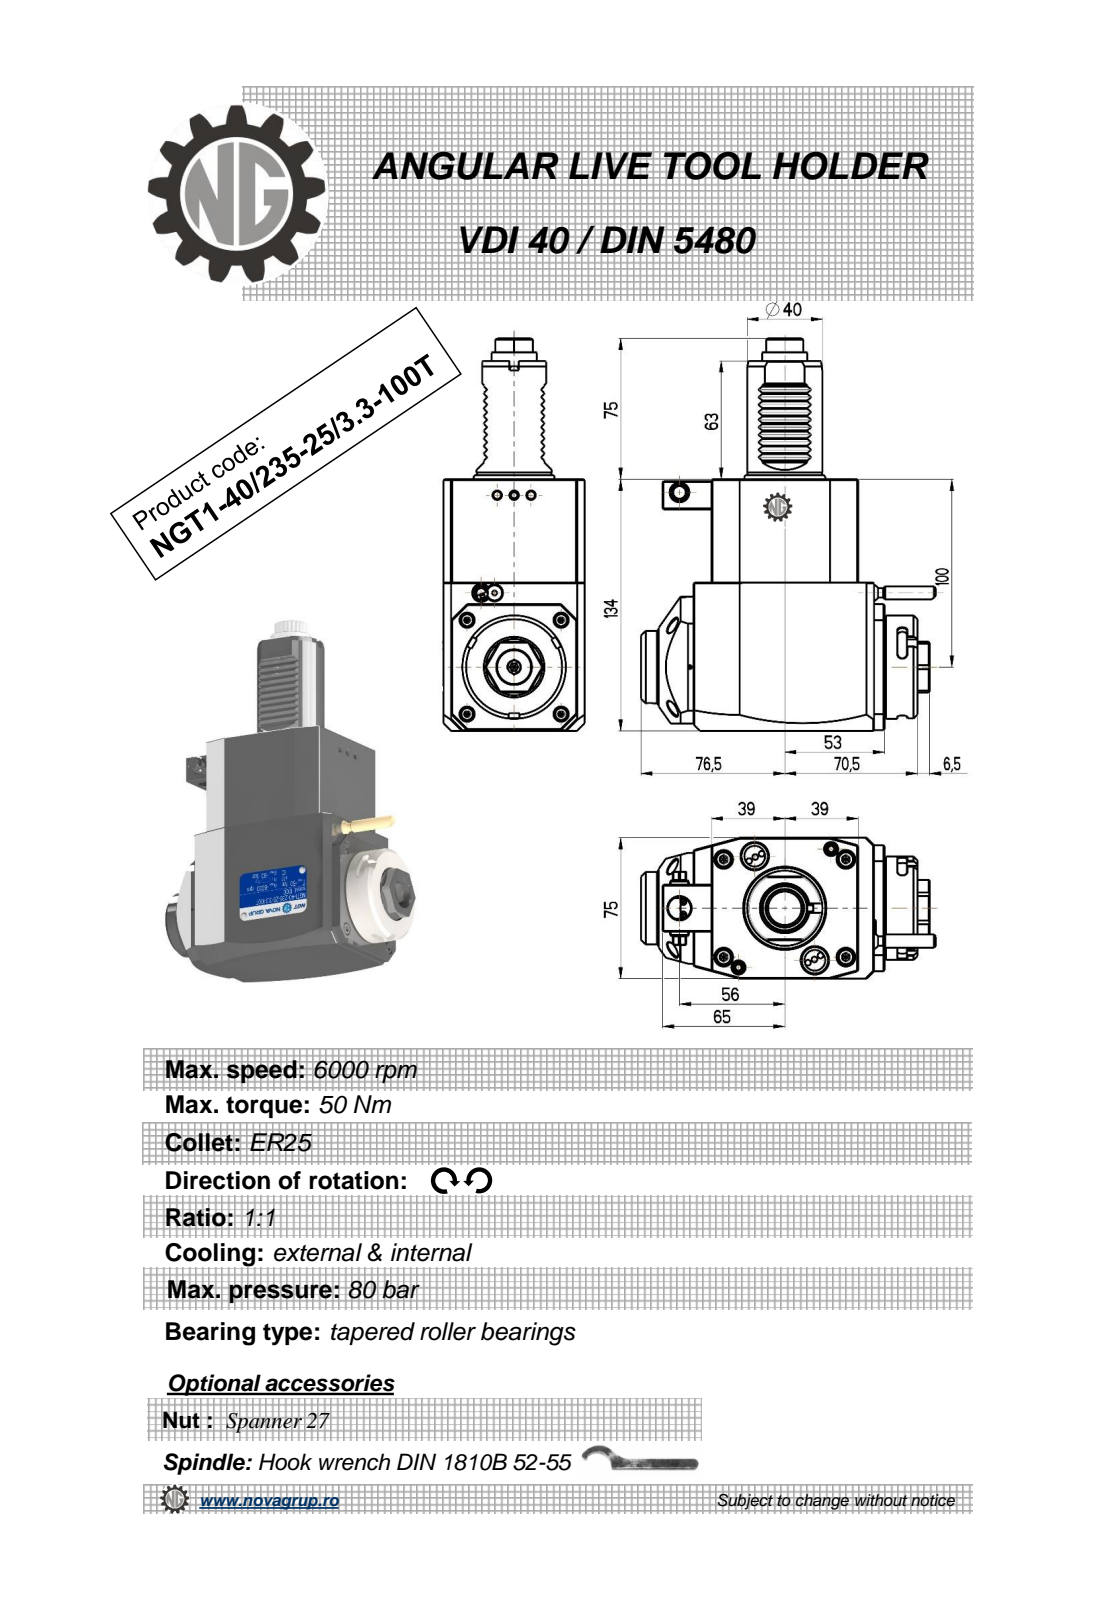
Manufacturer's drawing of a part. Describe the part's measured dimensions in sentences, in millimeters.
The part is named "NGT1_40_235_25_3_3_100T". Its 3-D file was written by "PRO/ENGINEER BY PARAMETRIC TECHNOLOGY CORPORATION, 2010280 (CONFIG_CONTROL_DESIGN)". It is 1 solid with 540 faces: 226 planar, 202 cylindrical and 112 other. Overall it measures 209 by 156.83 by 75 millimeters. Its volume is 1 080 000 cubic millimeters and its surface area 78 793 square millimeters. Round holes: 2 of diameter 3.3, 2 of diameter 4.5, 2 of diameter 7.5, 1 of diameter 2.5, 1 of diameter 3, 1 of diameter 9.5, 1 of diameter 12, 1 of diameter 18. Round bosses or shafts: 2 of diameter 8, 1 of diameter 55, 1 of diameter 48, 1 of diameter 40, 1 of diameter 38.5, 1 of diameter 24, 1 of diameter 10, 1 of diameter 7. Partial cylindrical surfaces (rounded edges, fillets, slot ends): 48 of radius 2.08, 20 of radius 0.3, 6 of radius 2.5, 2 of radius 15, 2 of radius 180, 1 of radius 3.85, 1 of radius 4.25, 1 of radius 9.08. The main face-to-face distances are 75, 134, 78, 14, 92, 17.5, 31.5, 79, 84.88, 109.5. The hole center spacings are 31.11, 18.07, 43.2, 54.87, 62.23, 72.9, 73.09, 91.5.
